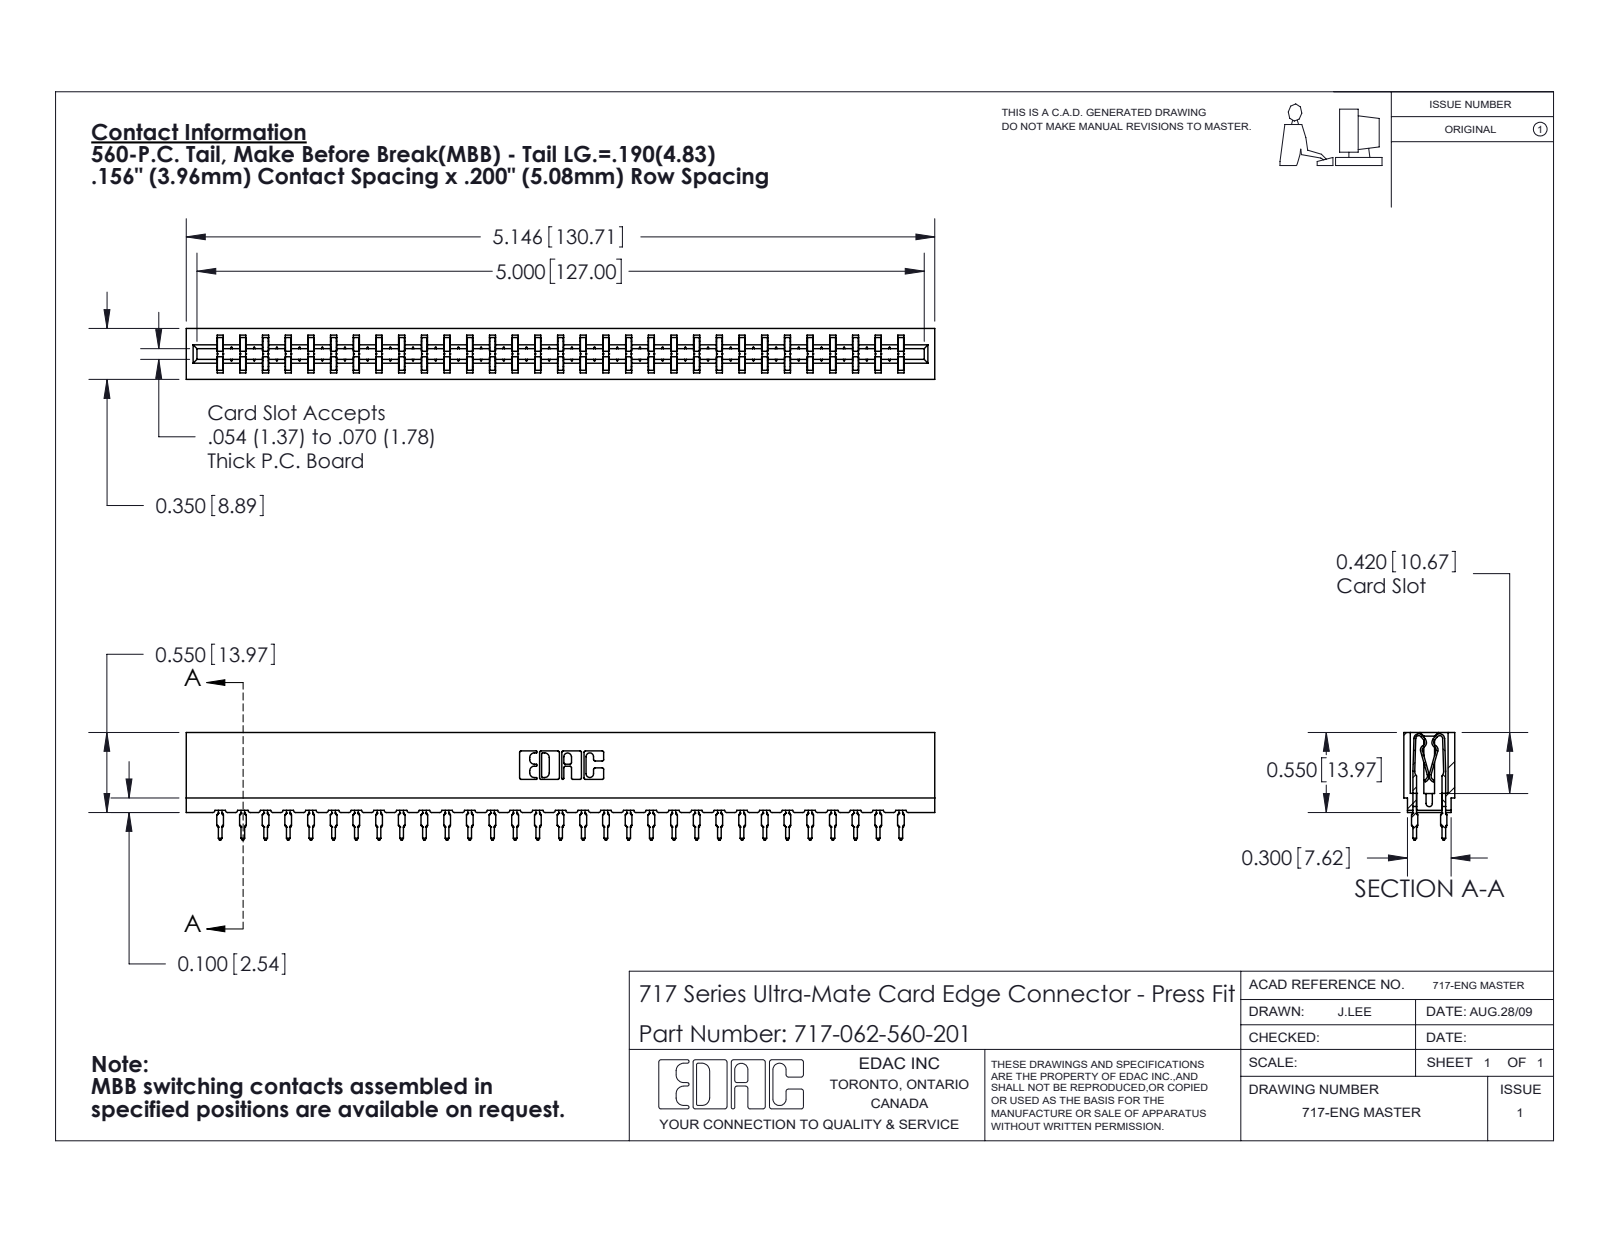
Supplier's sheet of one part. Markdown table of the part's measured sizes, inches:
| quantity | value |
| --- | --- |
| part name | 745-292-001_560; 717-062-560-201; 717 Part_Insulator Option - 06 |
| STEP written by | SolidWorks 2020 (CONFIG_CONTROL_DESIGN) |
| units | inches |
| bodies | 63 solids, 6232 faces (3247 planar, 1373 cylindrical, 1612 other) |
| overall size | 5.146 × 0.739 × 0.35 |
| volume | 0.708 in³ |
| surface area | 28.97 in² |
| partial cylindrical surfaces (radius × count) | 0.021 × 124, 0.015 × 62, 0.01 × 22, 0.005 × 8, 0.011 × 8, 0.007 × 6, 0.031 × 6, 0.026 × 3 |
| main face-to-face distances | 0.212, 0.138, 0.35, 0.063, 0.287, 0.076, 0.149, 0.074, 0.045, 0.305 |
